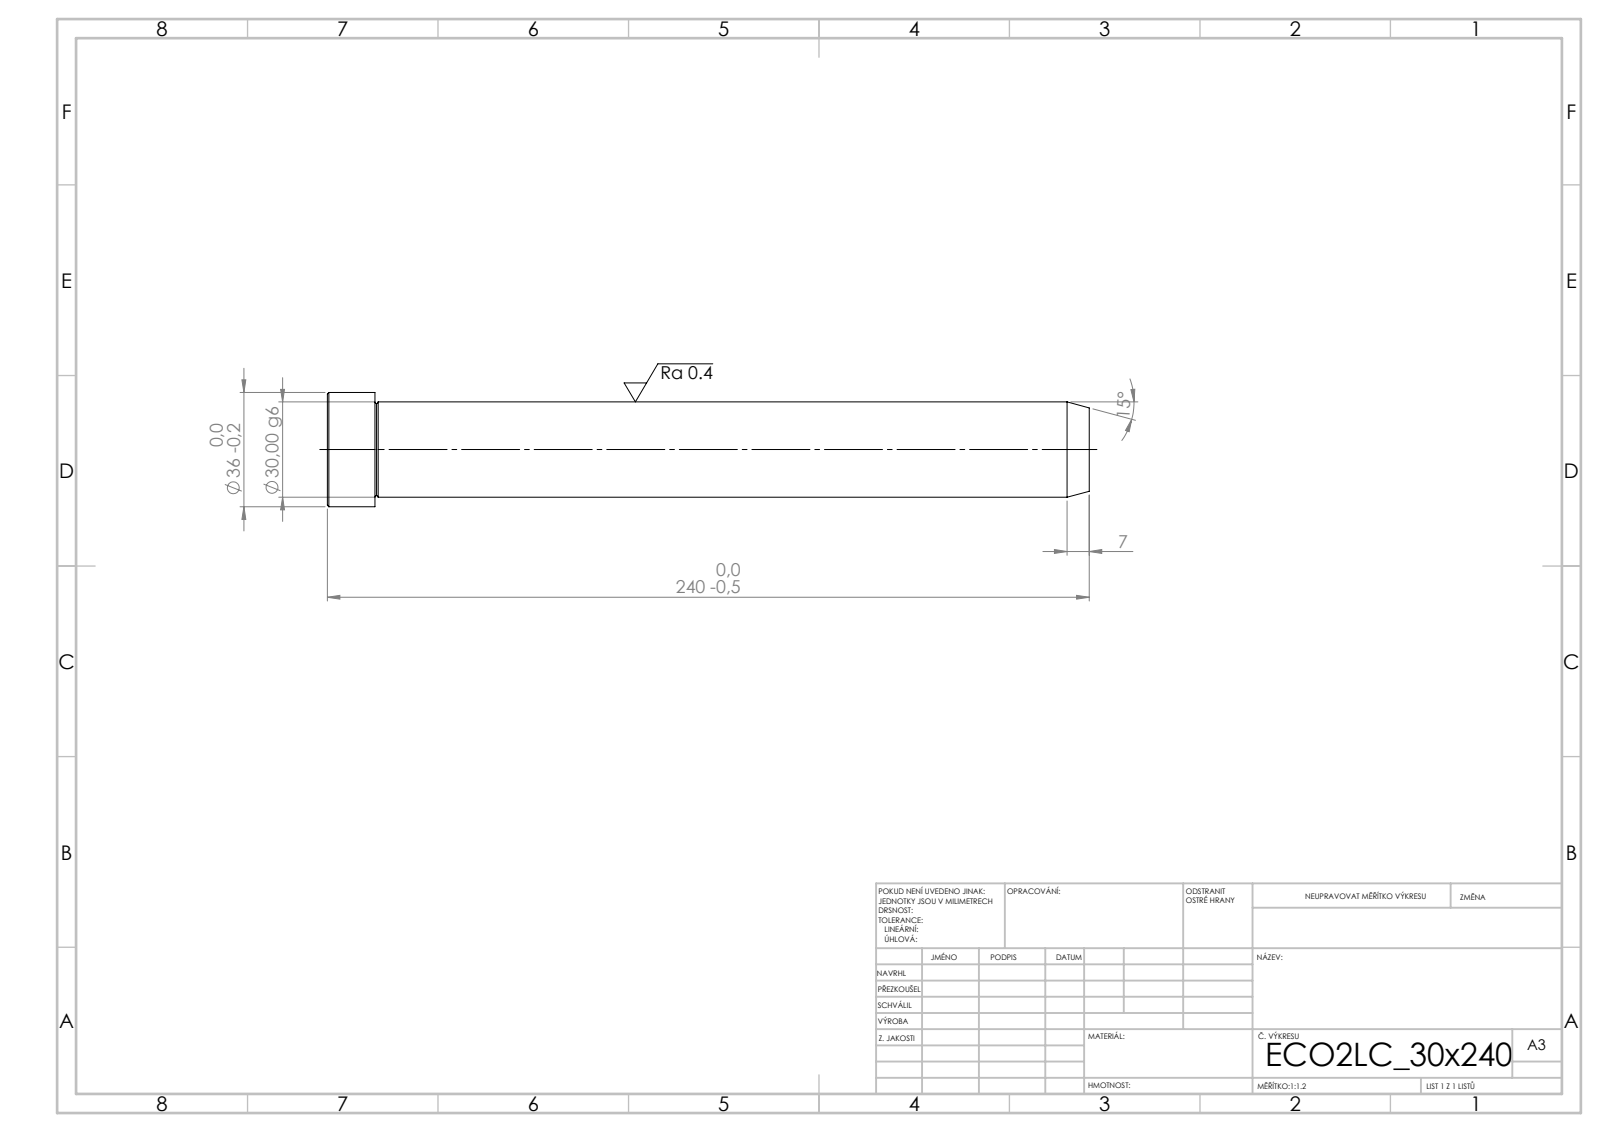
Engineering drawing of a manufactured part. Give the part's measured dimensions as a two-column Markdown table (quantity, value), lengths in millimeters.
| quantity | value |
| --- | --- |
| STEP written by | SolidWorks 2019 (CONFIG_CONTROL_DESIGN) |
| units | millimeters |
| bodies | 1 solid, 15 faces (3 planar, 4 cylindrical, 8 other) |
| overall size | 240 × 36 × 36 |
| volume | 173 668 mm³ |
| surface area | 24 770 mm² |
| round bosses / shafts (diameter × count) | 36 × 1, 30 × 1 |
| main face-to-face distances | 240, 225, 15 |
